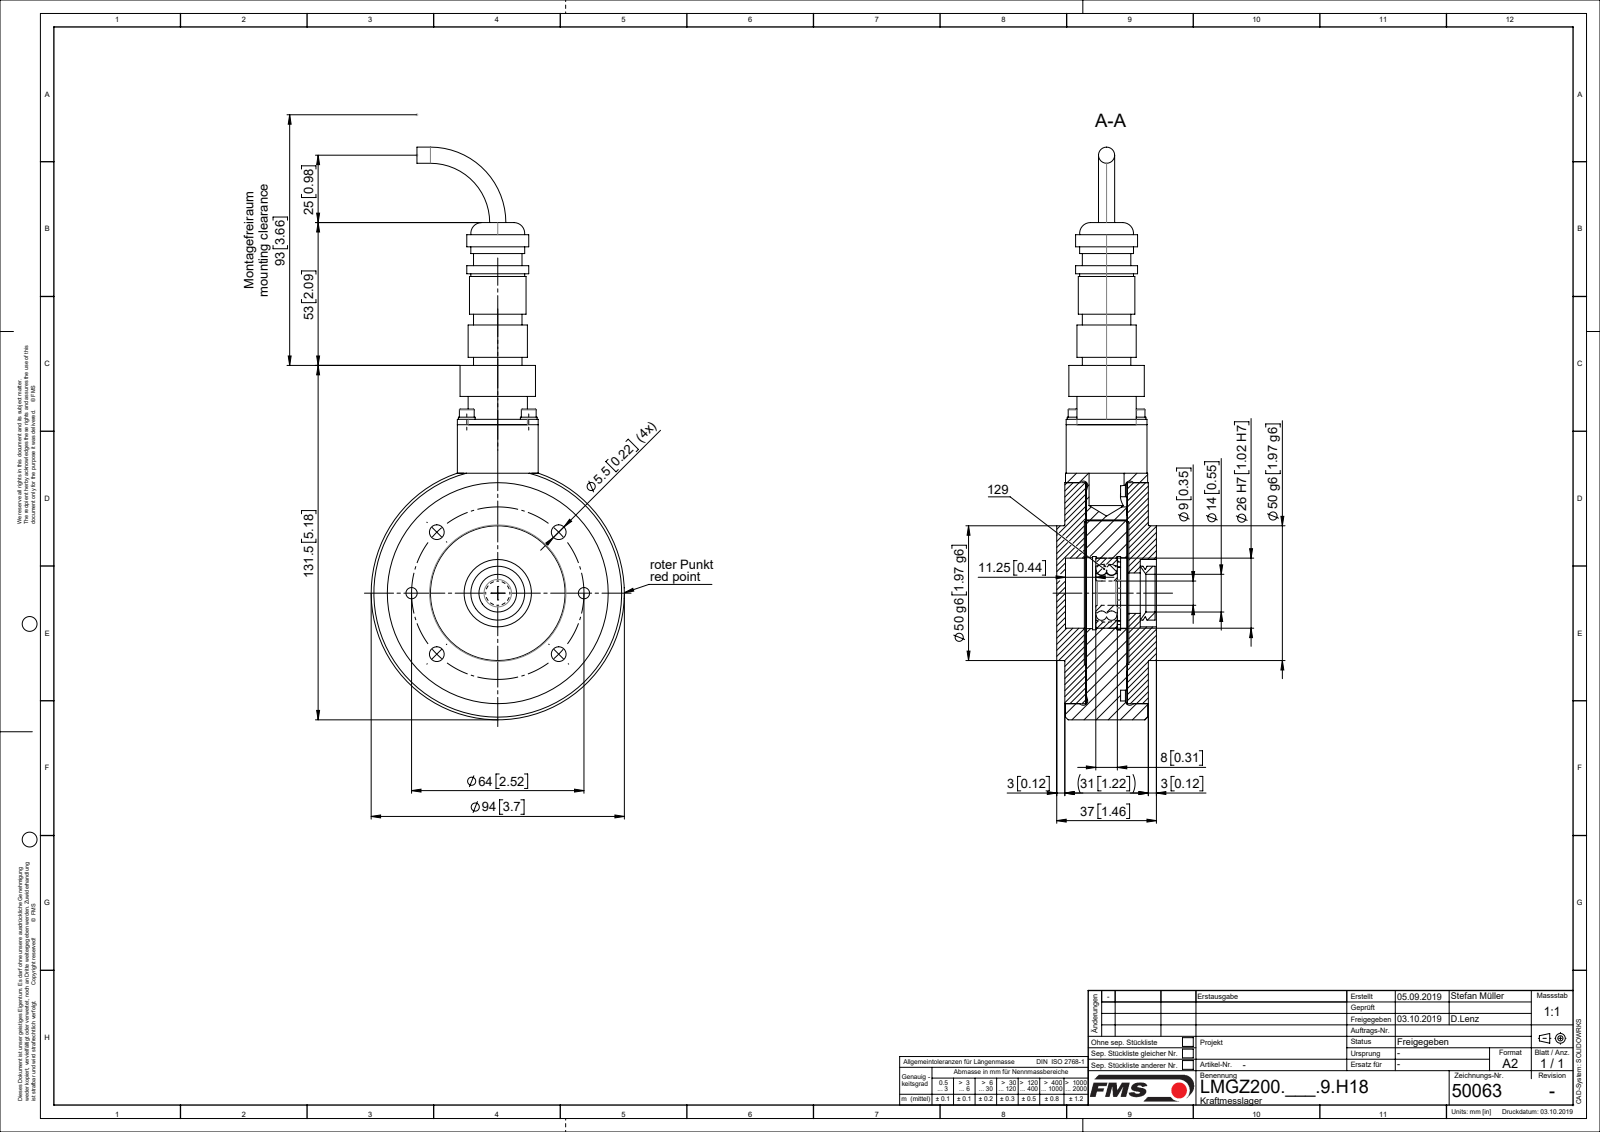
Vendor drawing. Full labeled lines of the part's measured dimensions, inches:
Part name (STEP PRODUCT): L50063; L4900504; L49012; TEIL1 (+8 more)
STEP written by: Mechanical Desktop 2007 (CONFIG_CONTROL_DESIGN)
Units: inches
Bodies: 20 solids, 378 faces (101 planar, 231 cylindrical, 46 other)
Overall size (bounding box): 8.366 × 3.819 × 1.457
Volume: 15.16 in³ · Surface area: 138.3 in²
Round holes (diameter × count): ⌀0.217 ×6, ⌀0.102 ×4, ⌀0.126 ×4, ⌀0.134 ×4, ⌀0.17 ×4, ⌀0.26 ×4, ⌀0.394 ×2, ⌀0.354 ×1, ⌀0.551 ×1, ⌀0.591 ×1, ⌀0.634 ×1, ⌀0.984 ×1
Round bosses / shafts (diameter × count): ⌀0.244 ×4, ⌀0.217 ×4, ⌀0.118 ×4, ⌀0.098 ×4, ⌀0.787 ×2, ⌀0.315 ×2, ⌀0.197 ×2, ⌀3.701 ×1
Partial cylindrical surfaces — rounded edges, fillets, slot ends (radius × count): R0.157 ×4, R0.315 ×2
Main face-to-face distances: 0.6, 0.591, 0.915, 0.906, 0.305, 0.315, 0.61, 0.02, 0.285, 0.433
Hole centre spacings: 1.26, 0.906, 0.964, 1.782, 2.328, 2.471, 0.491, 0.492
